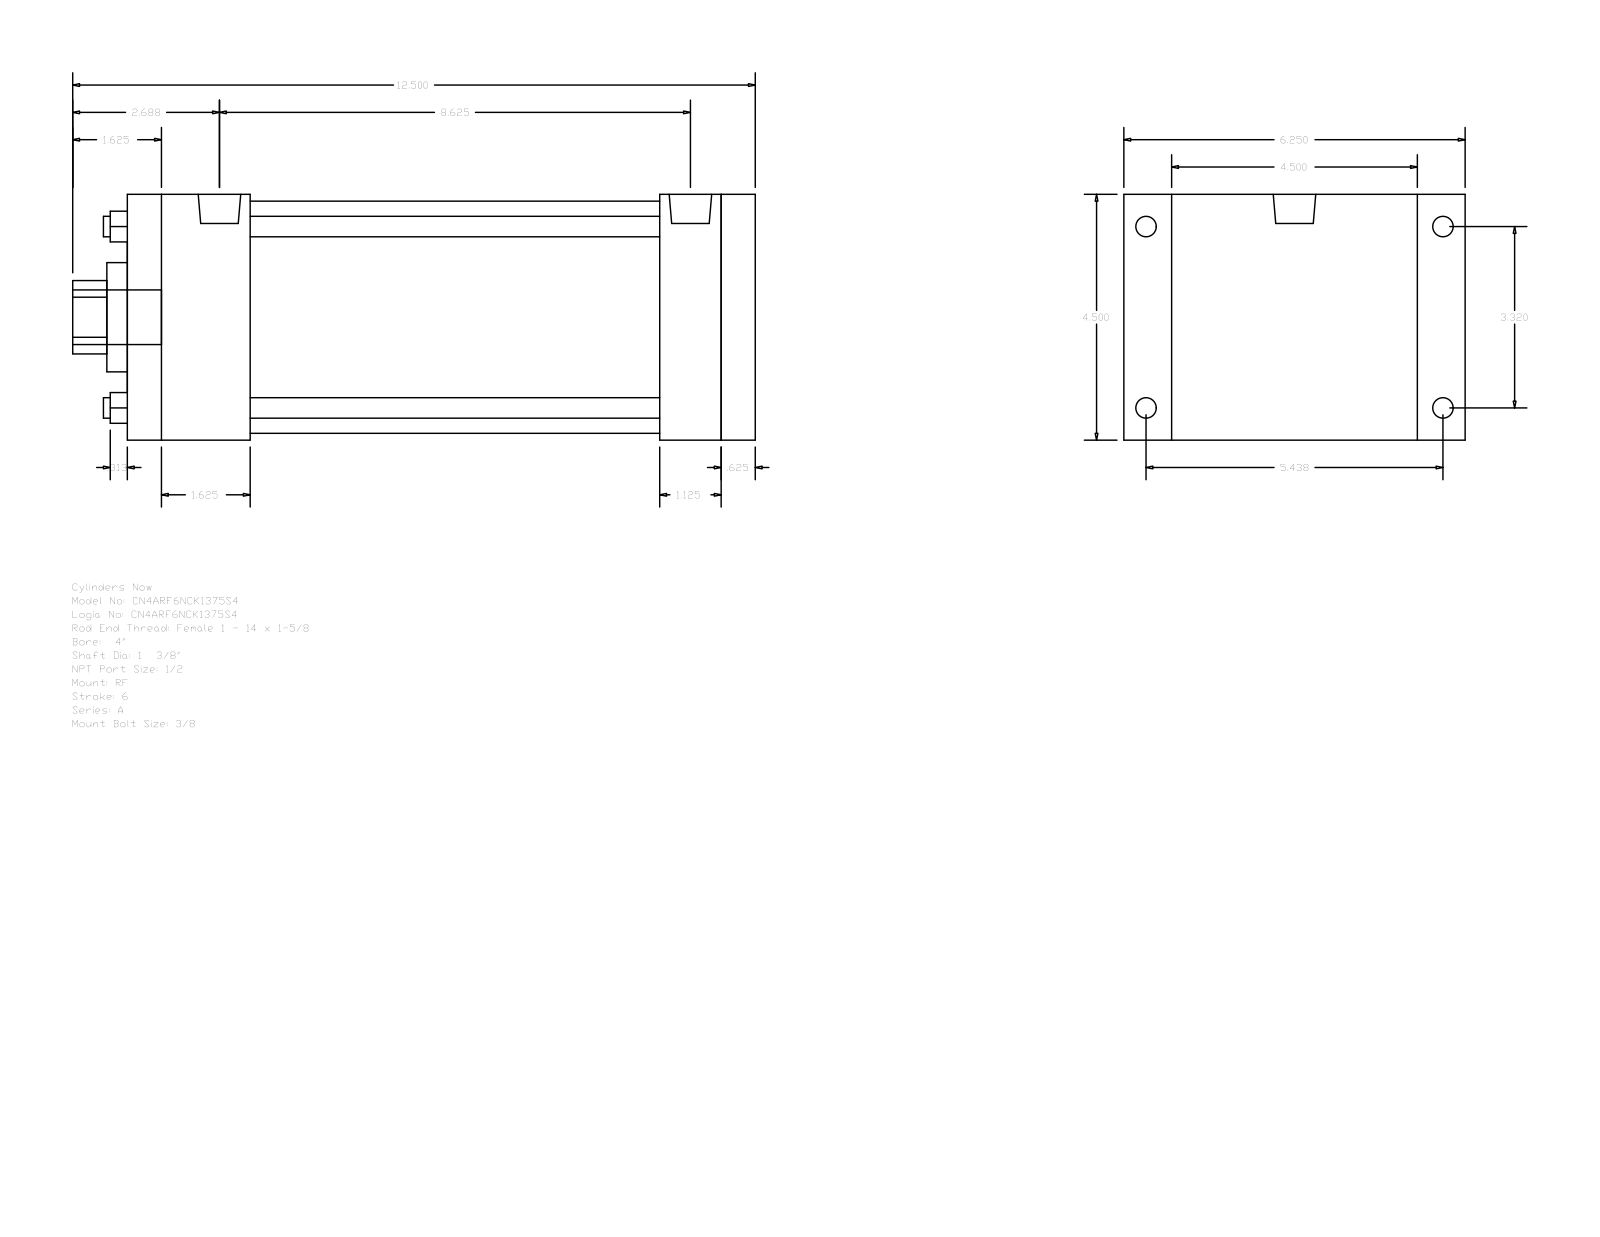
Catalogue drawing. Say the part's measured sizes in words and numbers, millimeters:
The part is named "A_RF__0400_1.375". Its 3-D file was written by "GSSL Pune (CONFIG_CONTROL_DESIGN)". It is 0 solids with 92 faces: 64 planar, 28 cylindrical and 0 other. Overall it measures 317.5 by 158.75 by 114.3 millimeters. Round holes: 4 of diameter 9.53, 1 of diameter 34.92, 1 of diameter 50.8, 1 of diameter 107.95. Round bosses or shafts: 4 of diameter 9.53, 4 of diameter 8.73, 2 of diameter 19.77, 1 of diameter 25.4. Partial cylindrical surfaces (rounded edges, fillets, slot ends): 1 of radius 17.06. The main face-to-face distances are 114.3, 292.1, 15.88, 276.22, 28.57, 22.23, 136.53, 247.65, 44.45, 57.15. The hole center spacings are 59.62, 84.32, 119.25.
